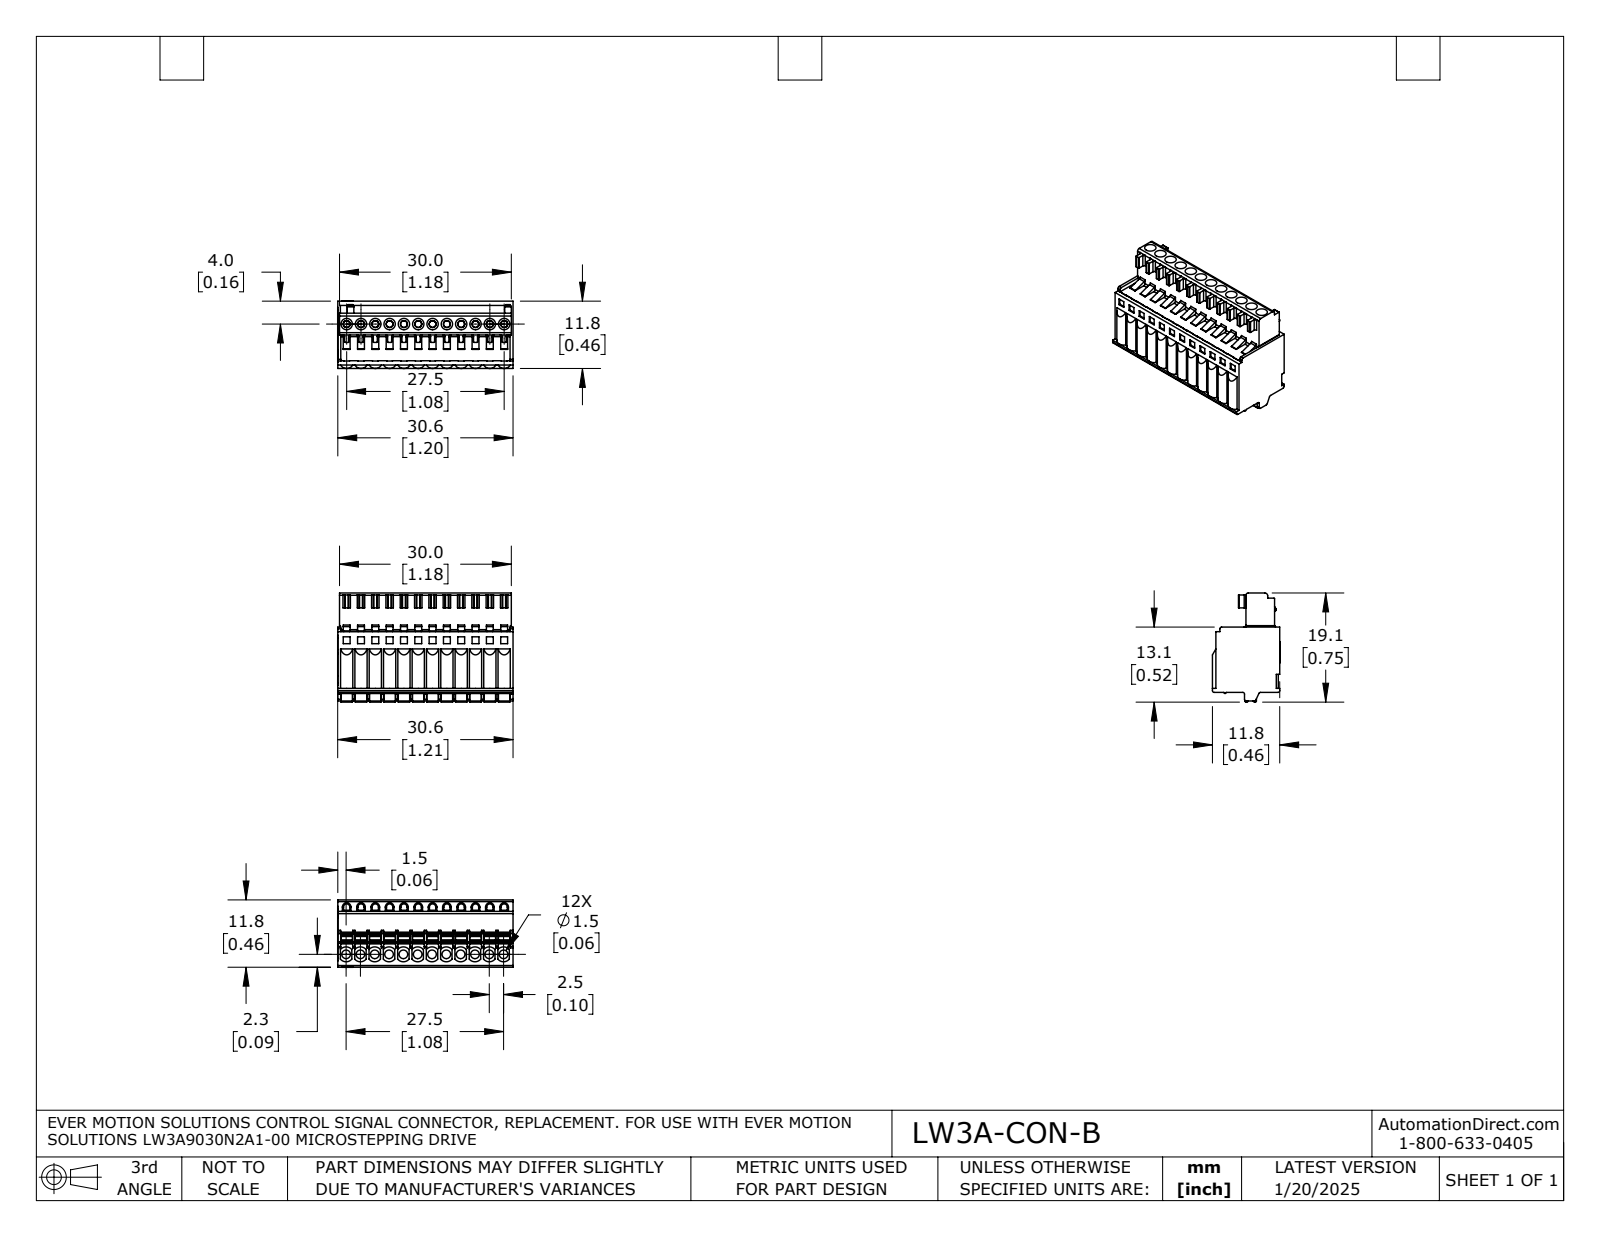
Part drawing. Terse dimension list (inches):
name: LW3A-CON-B
written by: SolidWorks 2021 (AUTOMOTIVE_DESIGN)
unit: in
bodies: 37 solids, 1782 faces (1245 planar, 426 cylindrical, 111 other)
size: 1.206 × 0.75 × 0.463
volume: 0.251 in³; area: 7.732 in²
holes: 12× ⌀0.046, 12× ⌀0.047, 12× ⌀0.059
rounds: 35× R0.012, 25× R0.004, 12× R0.022, 12× R0.049, 12× R0.051, 12× R0.079, 8× R0.008, 5× R0.02
face distances: 0.079, 0.232, 0.098, 0.156, 0.239, 0.16, 0.072, 0.15, 0.197, 0.078
hole spacings: 0.098, 0.197, 0.295, 0.591, 0.394, 0.492, 0.069, 0.117
